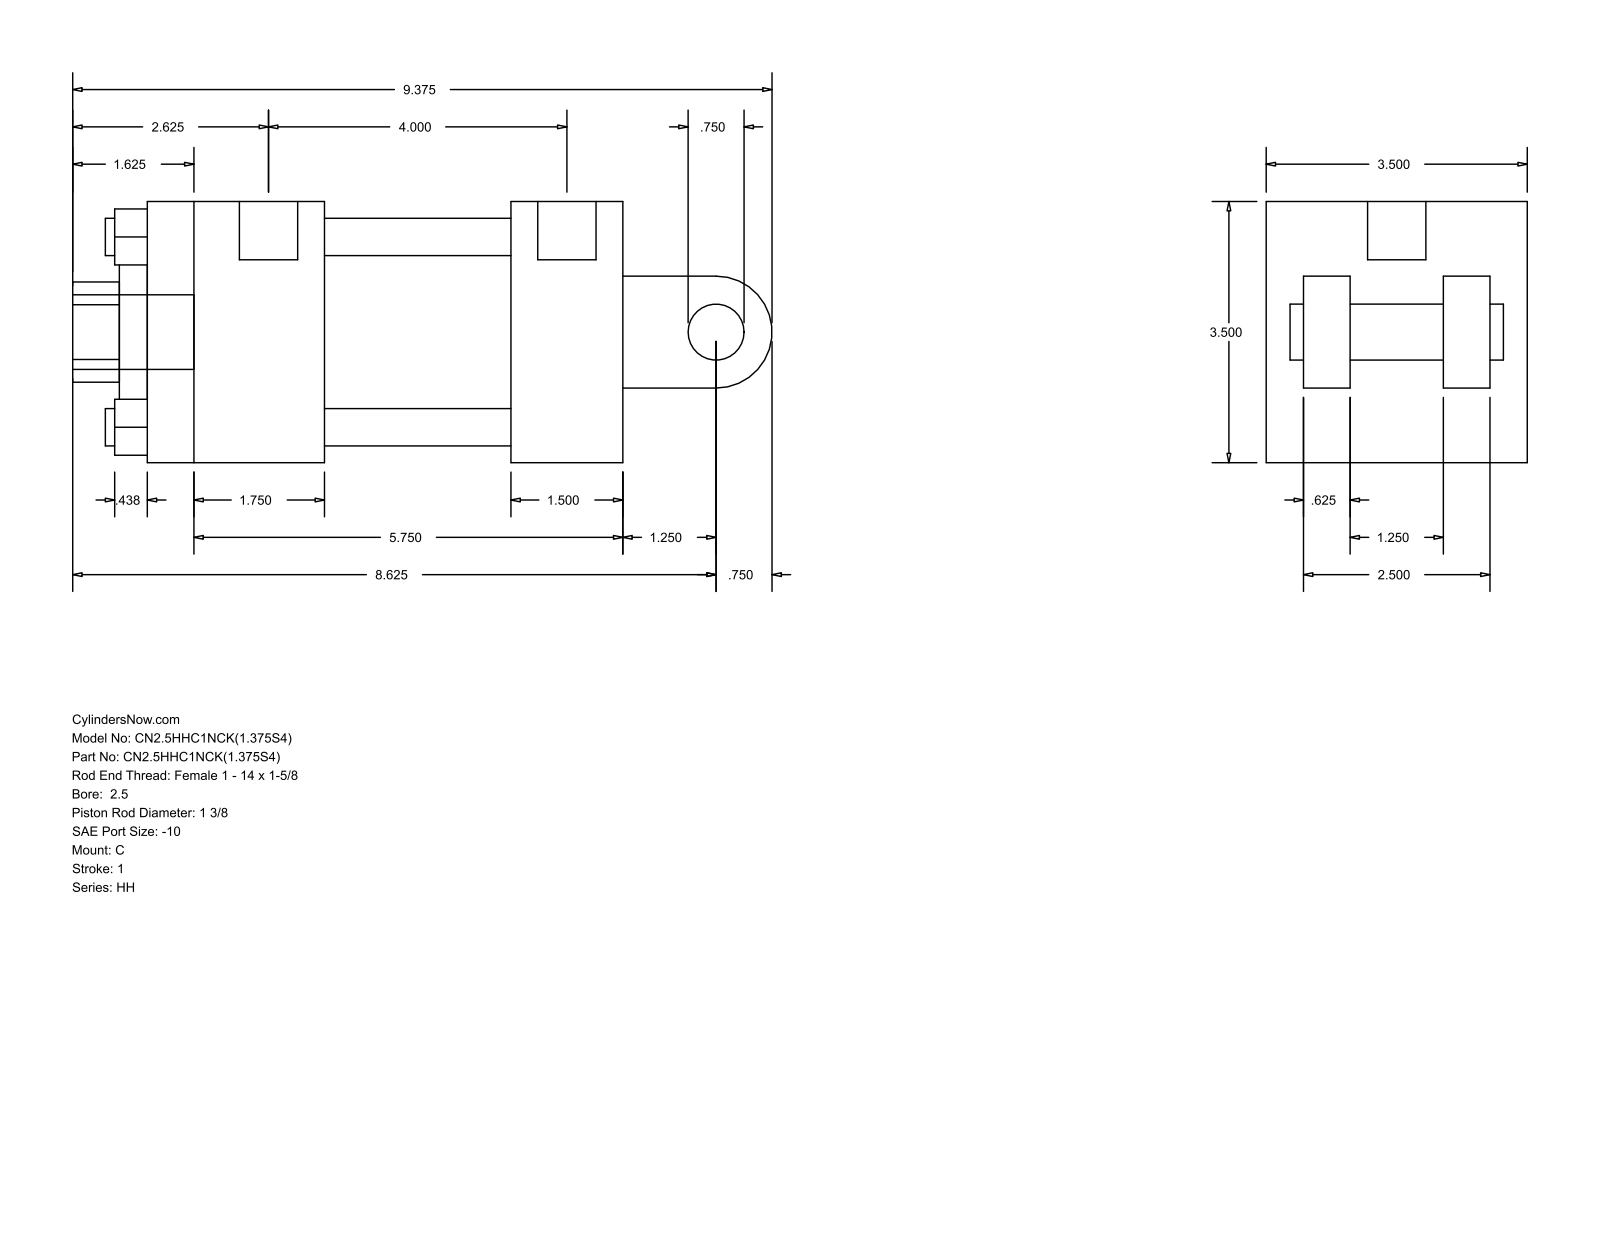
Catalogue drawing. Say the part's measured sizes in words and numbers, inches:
The part is named "HH_C__0250_1.375". Its 3-D file was written by "GSSL Pune (CONFIG_CONTROL_DESIGN)". It is 0 solids with 99 faces: 70 planar, 29 cylindrical and 0 other. Overall it measures 9.375 by 3.5 by 3.5 inches. Round holes: 4 of diameter 0.5, 2 of diameter 0.219, 1 of diameter 0.781, 1 of diameter 1.375, 1 of diameter 2, 1 of diameter 2.875. Round bosses or shafts: 2 of diameter 0.219, 1 of diameter 1, 1 of diameter 0.781, 1 of diameter 0.75. Partial cylindrical surfaces (rounded edges, fillets, slot ends): 1 of radius 0.672, 1 of radius 0.75. The main face-to-face distances are 3.5, 2.5, 6.375, 1.5, 0.625, 0.5, 4.875, 2.375, 4, 1.125. The hole center spacings are 1.803, 2.55, 3.606, 0.062.
